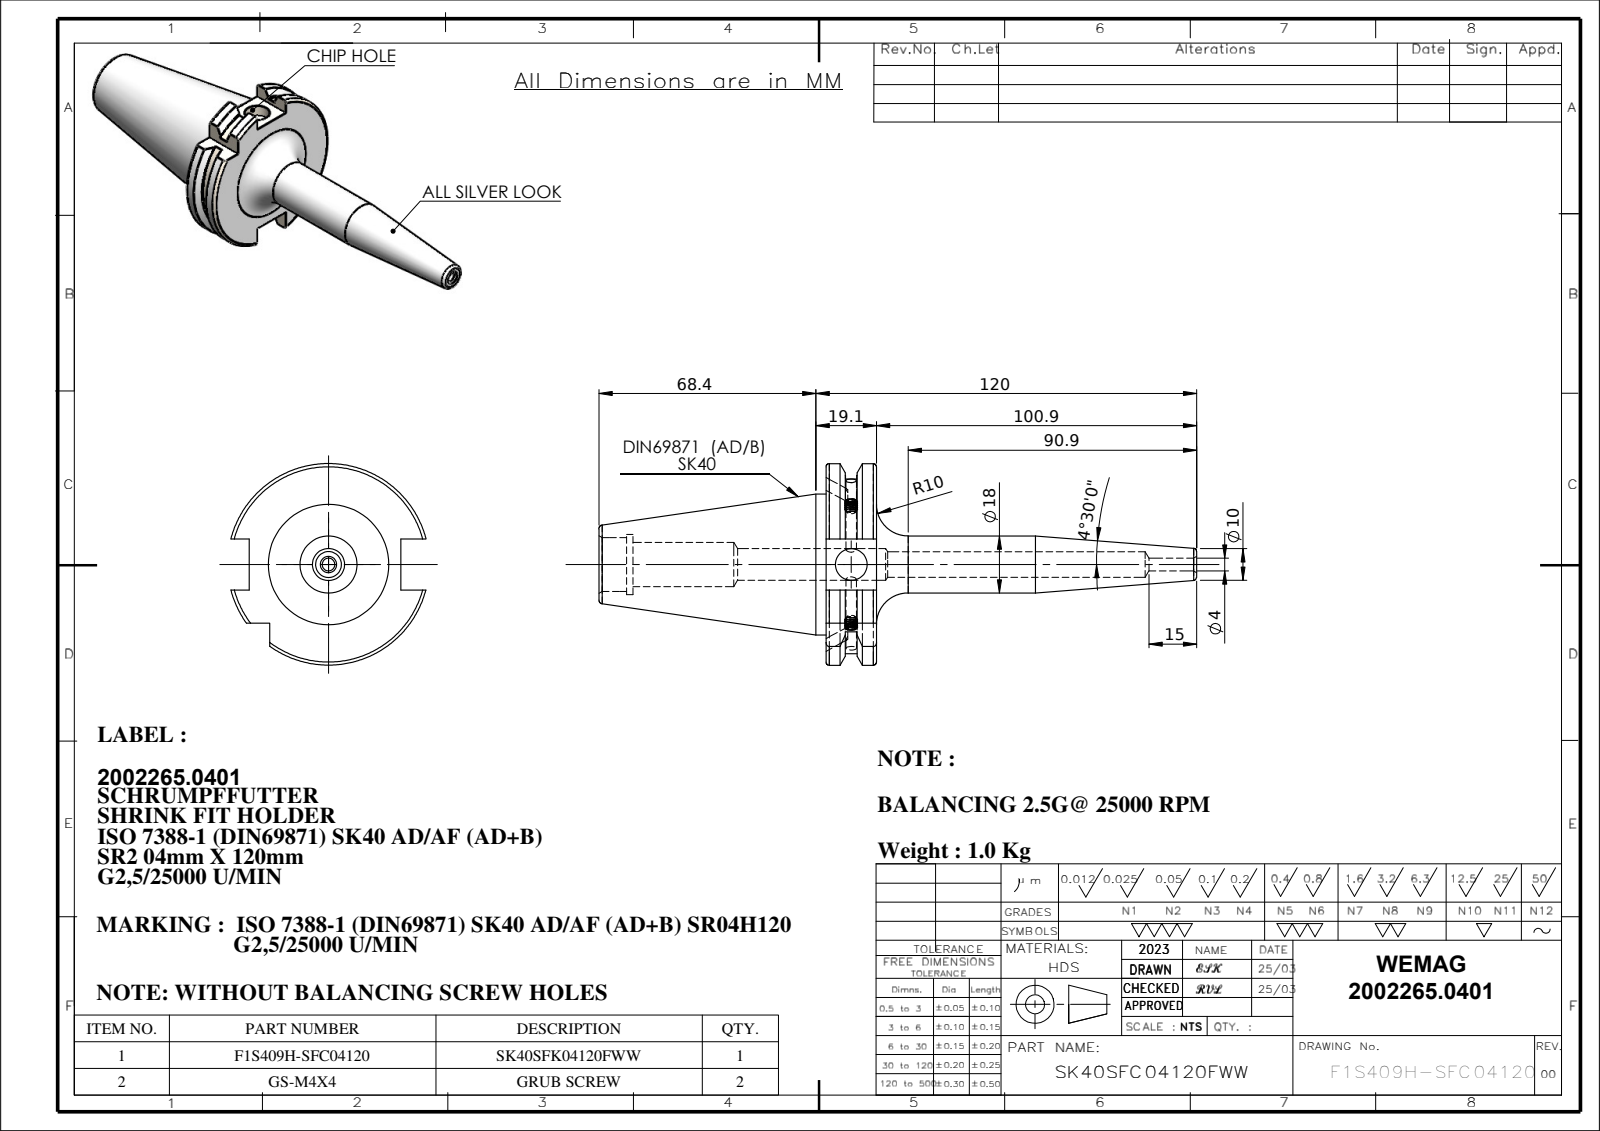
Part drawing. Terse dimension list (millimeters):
name: GS-M4X4_DIN 913 - M4 x 4-N; SK40SFC04120FWW; 91406-SR204120
written by: SolidWorks 2018 (CONFIG_CONTROL_DESIGN)
unit: mm
bodies: 3 solids, 196 faces (46 planar, 54 cylindrical, 96 other)
size: 188.4 × 63.55 × 61.48
volume: 119 401 mm³; area: 28 205 mm²
holes: 2× ⌀10, 1× ⌀3.3, 1× ⌀3.99, 1× ⌀8, 1× ⌀14, 1× ⌀17, 1× ⌀19
bosses: 2× ⌀4, 1× ⌀44.45, 1× ⌀18
rounds: 1× R28.12, 1× R31.77
face distances: 15.9, 16.1, 47.8, 71.6, 87.5, 10.7, 60.9, 76.8, 77.63, 66.93
